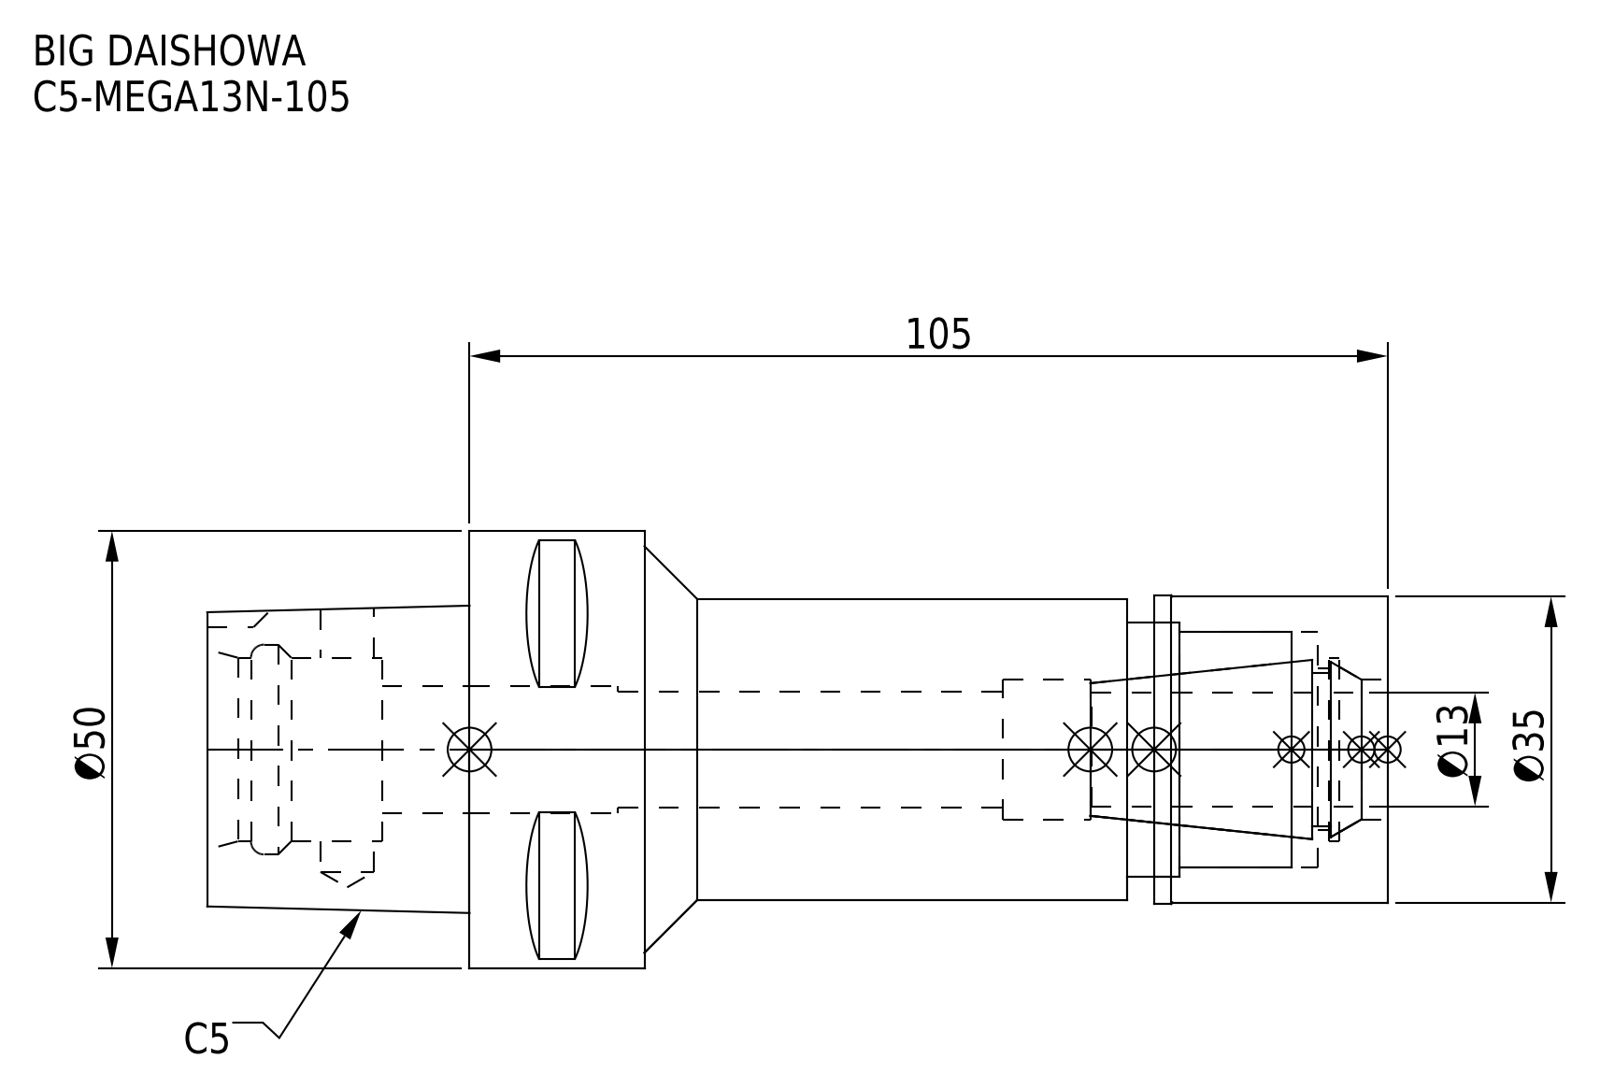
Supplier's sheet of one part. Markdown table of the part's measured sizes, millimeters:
| quantity | value |
| --- | --- |
| part name | C5-MEGA13N-105-130-FreeParts; MGN13_1.stp; C5-MEGA13N-105; C5-MEGA13N-105-130_ASM.stp (+3 more) |
| STEP written by | SolidWorks 2019 (CONFIG_CONTROL_DESIGN) |
| units | millimeters |
| bodies | 2 solids, 95 faces (38 planar, 39 cylindrical, 18 other) |
| overall size | 135 × 50 × 50 |
| volume | 117 788 mm³ |
| surface area | 30 356 mm² |
| round holes (diameter × count) | 6.1 × 1, 13.3 × 1, 14.5 × 1, 16 × 1, 18.5 × 1, 21 × 1, 24 × 1, 27 × 1, 29 × 1 |
| round bosses / shafts (diameter × count) | 50 × 1, 35.3 × 1, 35 × 1, 34.5 × 1 |
| partial cylindrical surfaces (radius × count) | 4 × 1 |
| main face-to-face distances | 105, 30, 20, 78.3, 108.3, 135, 26.7, 8, 18.7, 97 |
